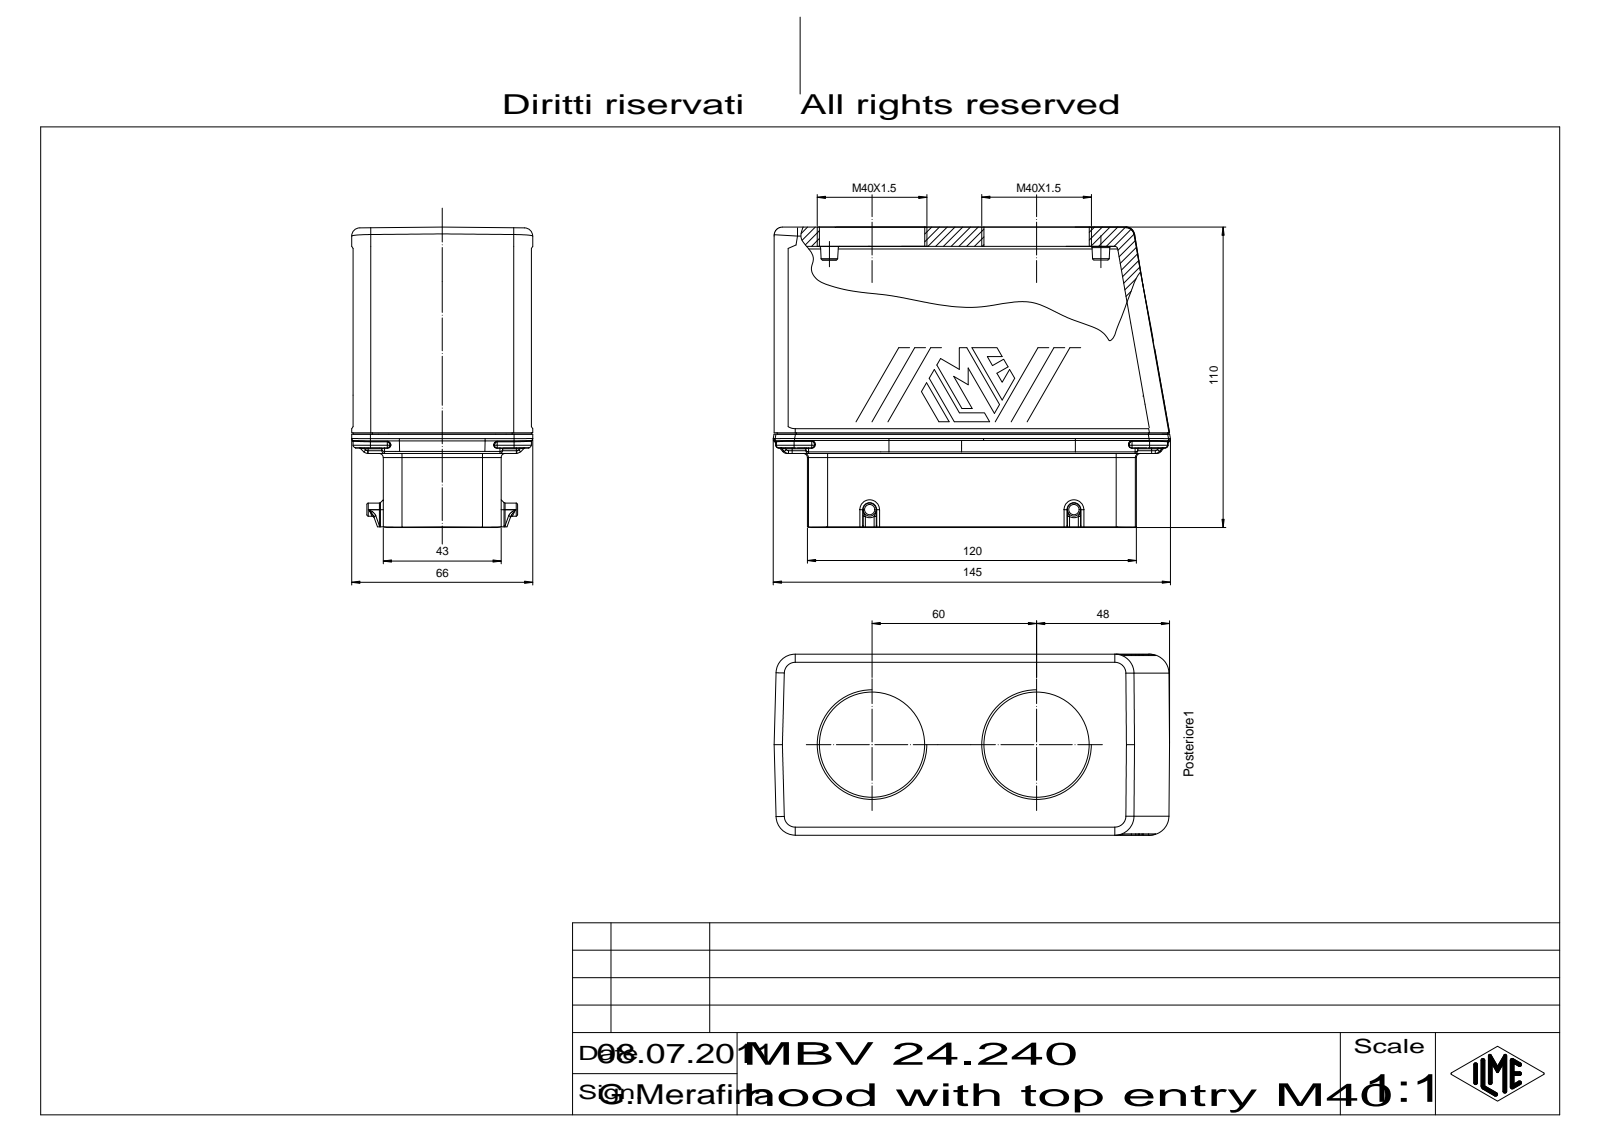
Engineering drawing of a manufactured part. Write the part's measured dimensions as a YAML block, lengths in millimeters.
part_name: "53848"
step_written_by: "CoCreate Modeling 16.00A 16-Aug-2008 (C) Parametric Technology GmbH (AUTOMOTIVE_DESIGN)"
units: millimeters
bodies: {solids: 1, faces: 693, planar: 377, cylindrical: 126, other: 190}
overall_size: [143.75, 108.97, 66.01]
volume: 681755
surface_area: 75134
round_holes:
  - {diameter: 40, count: 2}
round_bosses_or_shafts:
  - {diameter: 4.8, count: 2}
partial_cylinders:
  - {radius: 1, count: 44}
  - {radius: 7, count: 12}
  - {radius: 0.5, count: 8}
  - {radius: 0.3, count: 6}
  - {radius: 1.5, count: 6}
  - {radius: 3, count: 6}
  - {radius: 4.2, count: 4}
  - {radius: 5, count: 4}
face_to_face_distances: [65.01, 82.21, 0.4, 65.41, 11, 54.01, 54, 43, 11.01, 52.21]
hole_center_spacings: [60]
